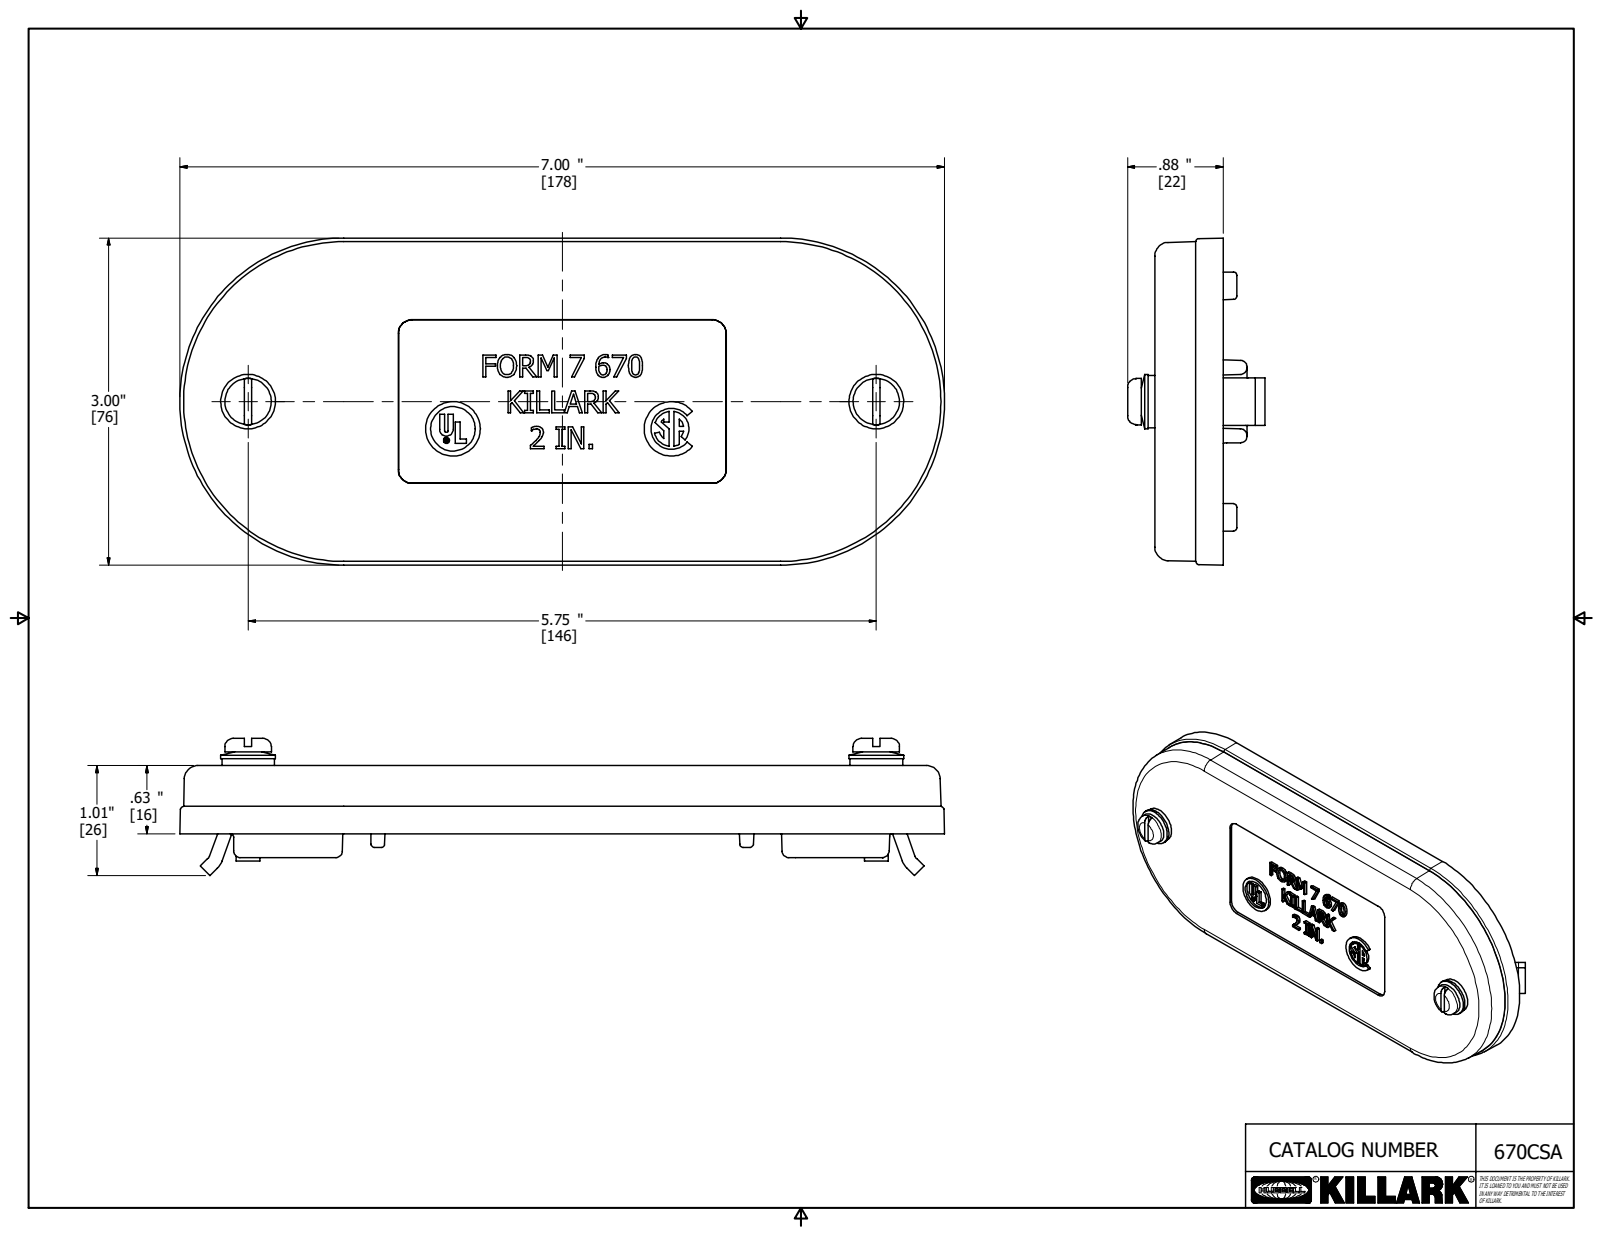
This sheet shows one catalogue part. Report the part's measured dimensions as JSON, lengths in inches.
{"part_name": "670CSA; 17716; 18038; 18033", "step_written_by": "Autodesk Inventor 2018 (AUTOMOTIVE_DESIGN)", "units": "inches", "bodies": {"solids": 7, "faces": 679, "planar": 341, "cylindrical": 144, "other": 194}, "overall_size": [7, 3, 1.258], "volume_in3": 6.364, "surface_area_in2": 66.97, "round_holes": [[0.177, 2], [0.047, 1], [0.407, 1]], "round_bosses_or_shafts": [[0.5, 3], [0.48, 2], [0.425, 2], [0.216, 2], [0.056, 1]], "partial_cylinders_radius": [[0.031, 32], [0.062, 25], [0.06, 13], [0.125, 6], [0.187, 5], [0.028, 2], [0.006, 1], [0.009, 1]], "face_to_face_distances": [0.219, 0.187, 0.031, 0.625, 0.594, 0.406, 0.222, 0.25, 0.028, 1.881], "hole_center_spacings": [0.122, 1.85, 1.892, 3.883, 3.951, 5.75]}
